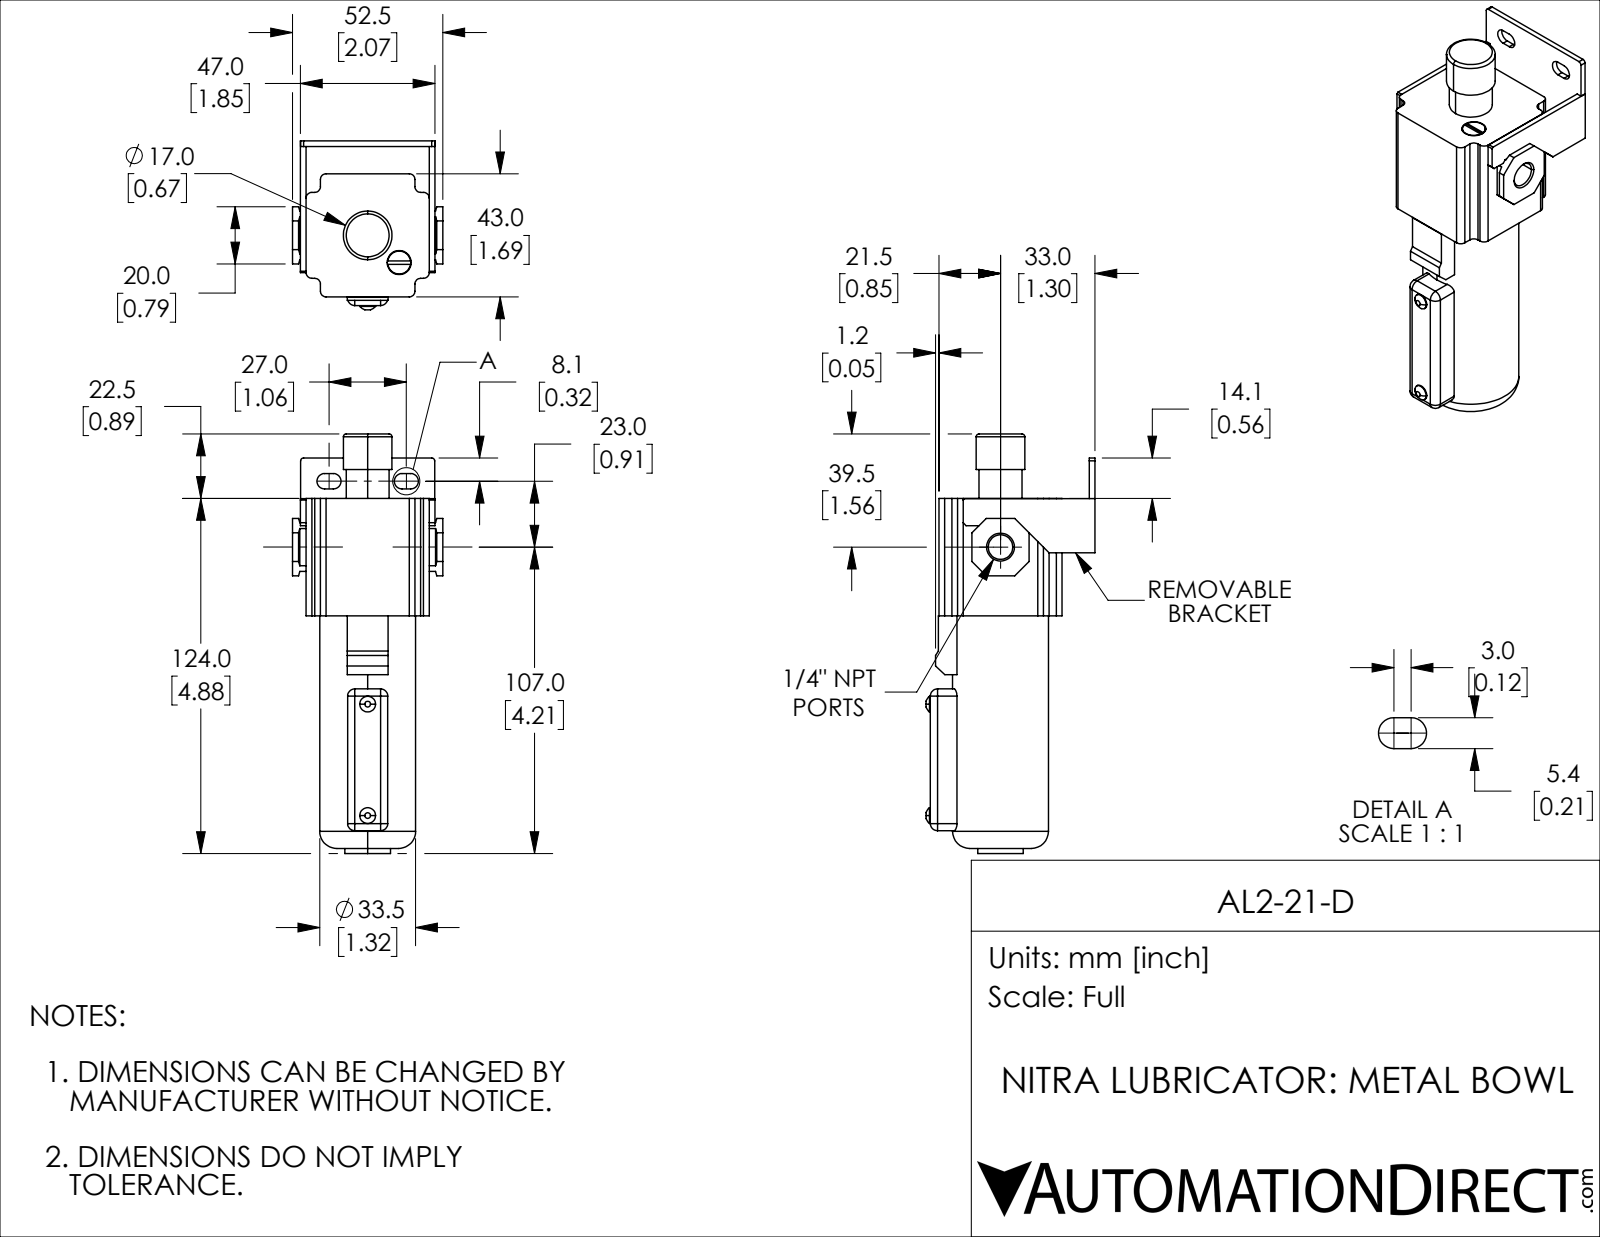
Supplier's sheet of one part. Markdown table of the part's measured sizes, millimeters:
| quantity | value |
| --- | --- |
| part name | AL2-21-D |
| STEP written by | SolidWorks 2019 (CONFIG_CONTROL_DESIGN) |
| units | millimeters |
| bodies | 1 solid, 164 faces (102 planar, 46 cylindrical, 16 other) |
| overall size | 146.5 × 59 × 52.5 |
| volume | 160 396 mm³ |
| surface area | 27 147 mm² |
| round holes (diameter × count) | 8.4 × 1, 8.57 × 1 |
| round bosses / shafts (diameter × count) | 5.5 × 2, 33.5 × 1, 17 × 1, 15.9 × 1, 15 × 1, 8 × 1 |
| partial cylindrical surfaces (radius × count) | 2 × 12, 2.5 × 8, 2.7 × 4, 1 × 2 |
| main face-to-face distances | 2, 43, 9.5, 52.5, 11.5, 54.5, 45, 41, 30.5, 14.5 |
